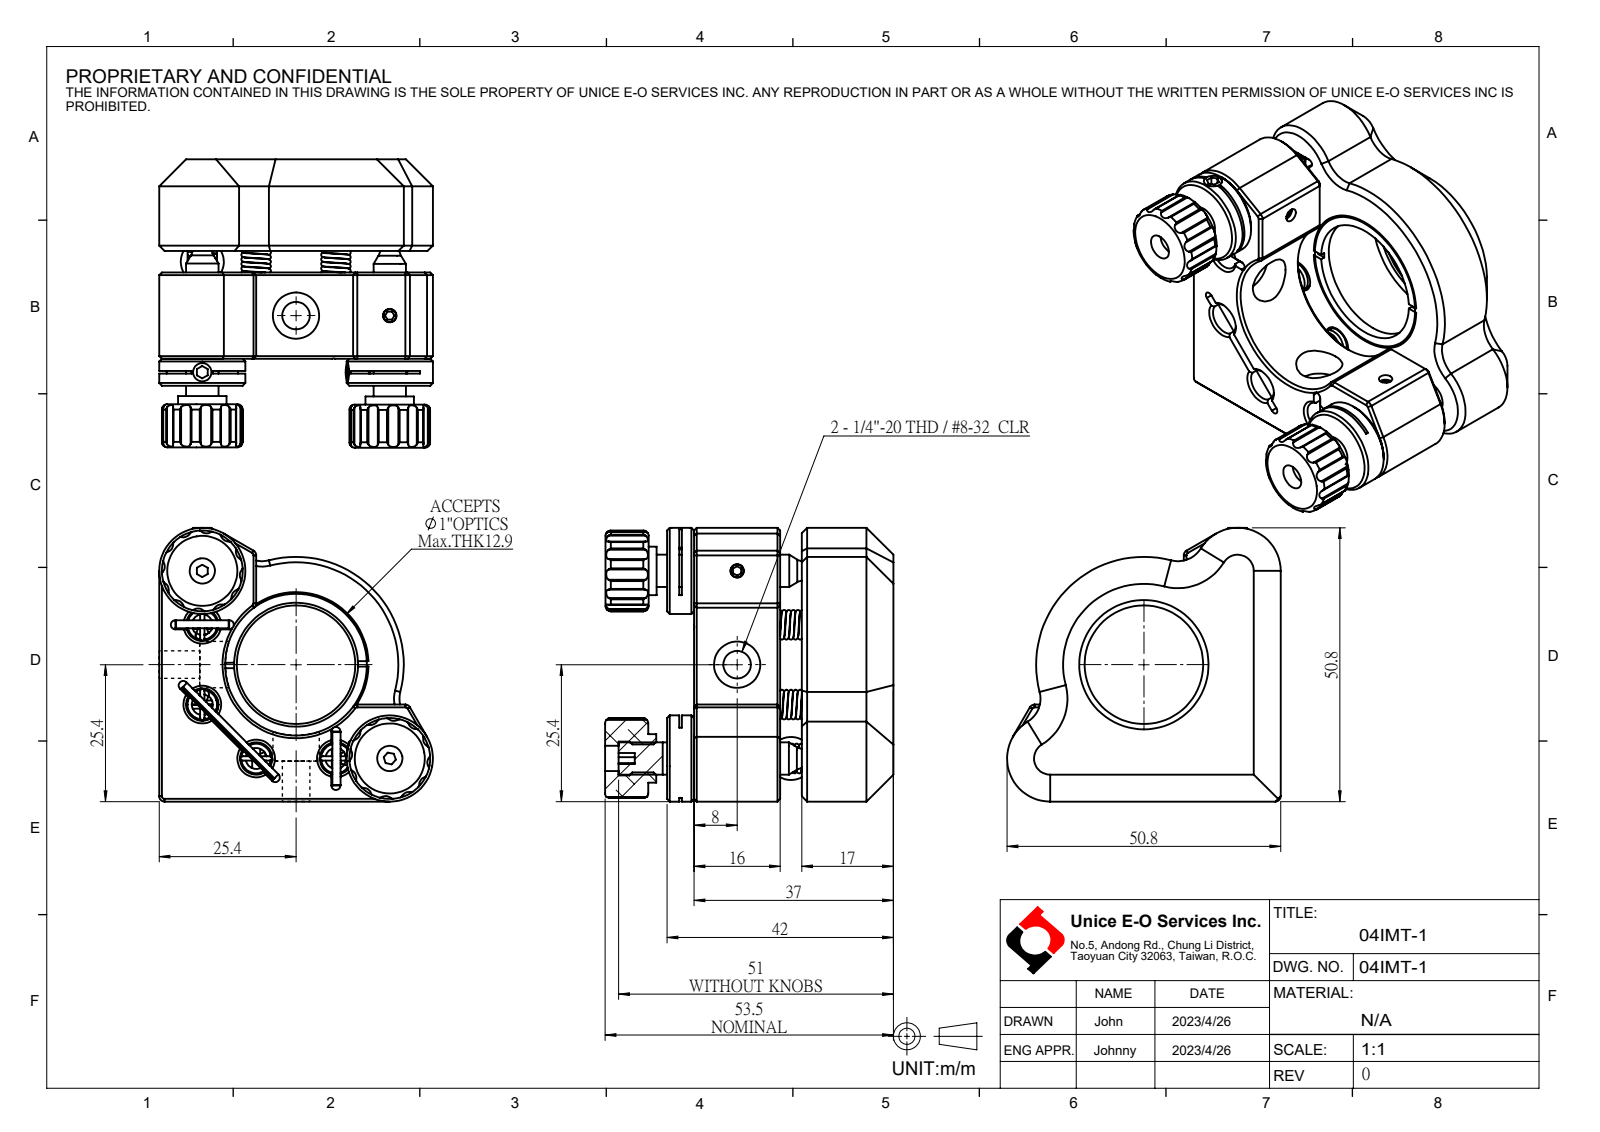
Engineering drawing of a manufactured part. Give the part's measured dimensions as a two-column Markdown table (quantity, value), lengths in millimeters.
| quantity | value |
| --- | --- |
| part name | 04IMT-1 |
| STEP written by | SolidWorks 2022 (CONFIG_CONTROL_DESIGN) |
| units | millimeters |
| bodies | 0 solids, 423 faces (114 planar, 210 cylindrical, 99 other) |
| overall size | 53.5 × 50.8 × 50.8 |
| round holes (diameter × count) | 1.7 × 4, 6 × 4, 2.5 × 2, 4.7 × 2, 5.11 × 2, 8.6 × 2, 10 × 2, 1.1 × 1, 22 × 1, 23 × 1, 24 × 1, 26.3 × 1 |
| round bosses / shafts (diameter × count) | 1.5 × 5, 16 × 2, 9 × 2, 6 × 2, 4 × 2 |
| partial cylindrical surfaces (radius × count) | 0.3 × 48, 1.5 × 25, 0.85 × 6, 1 × 5, 0.75 × 3, 5 × 2, 7.5 × 2, 20 × 1 |
| main face-to-face distances | 20.07, 16, 21.07, 17, 37.07, 4.07, 2.25, 2.75, 5, 21 |
| hole center spacings | 14.8, 18.91, 19.53, 10, 17.4, 20.65, 24.61, 24.8 |
